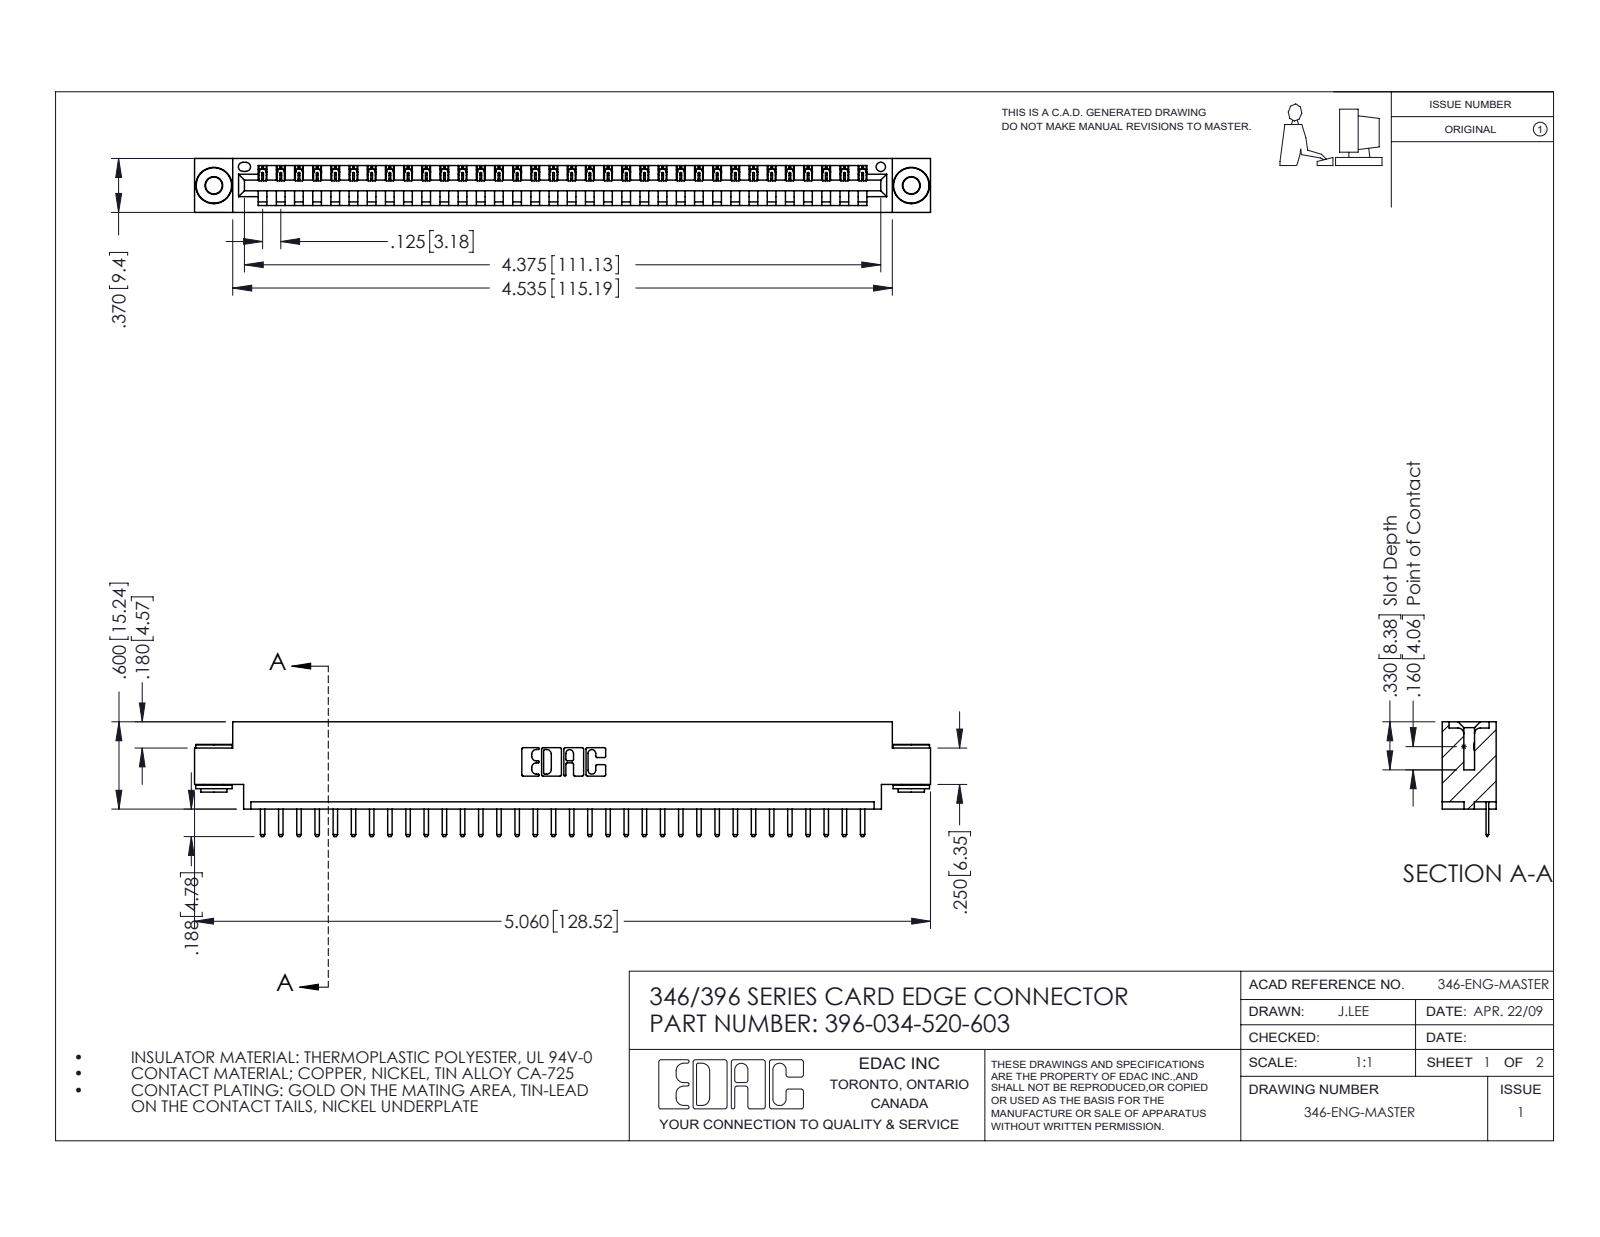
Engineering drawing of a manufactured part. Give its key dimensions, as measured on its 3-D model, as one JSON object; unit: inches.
{"part_name": "396-034-520-603; 345-292-001_345-293-120; 345-250-002_345-250-002-102; 346 Part_0.170 Offset - 0.156 Dia-TH", "step_written_by": "SolidWorks 2016 (CONFIG_CONTROL_DESIGN)", "units": "inches", "bodies": {"solids": 37, "faces": 2272, "planar": 1518, "cylindrical": 746, "other": 8}, "overall_size": [5.06, 0.788, 0.37], "volume_in3": 0.733, "surface_area_in2": 23.22, "round_holes": [[0.116, 2], [0.156, 2], [0.064, 1]], "round_bosses_or_shafts": [[0.25, 2], [0.18, 2], [0.136, 2]], "partial_cylinders_radius": [[0.01, 70], [0.006, 68], [0.01, 22], [0.007, 6], [0.031, 6], [0.026, 3], [0.031, 2], [0.04, 2]], "face_to_face_distances": [0.048, 0.322, 0.37, 0.25, 0.025, 0.148, 0.222, 0.1, 0.174, 0.072], "hole_center_spacings": [0.246, 4.587, 4.795]}
